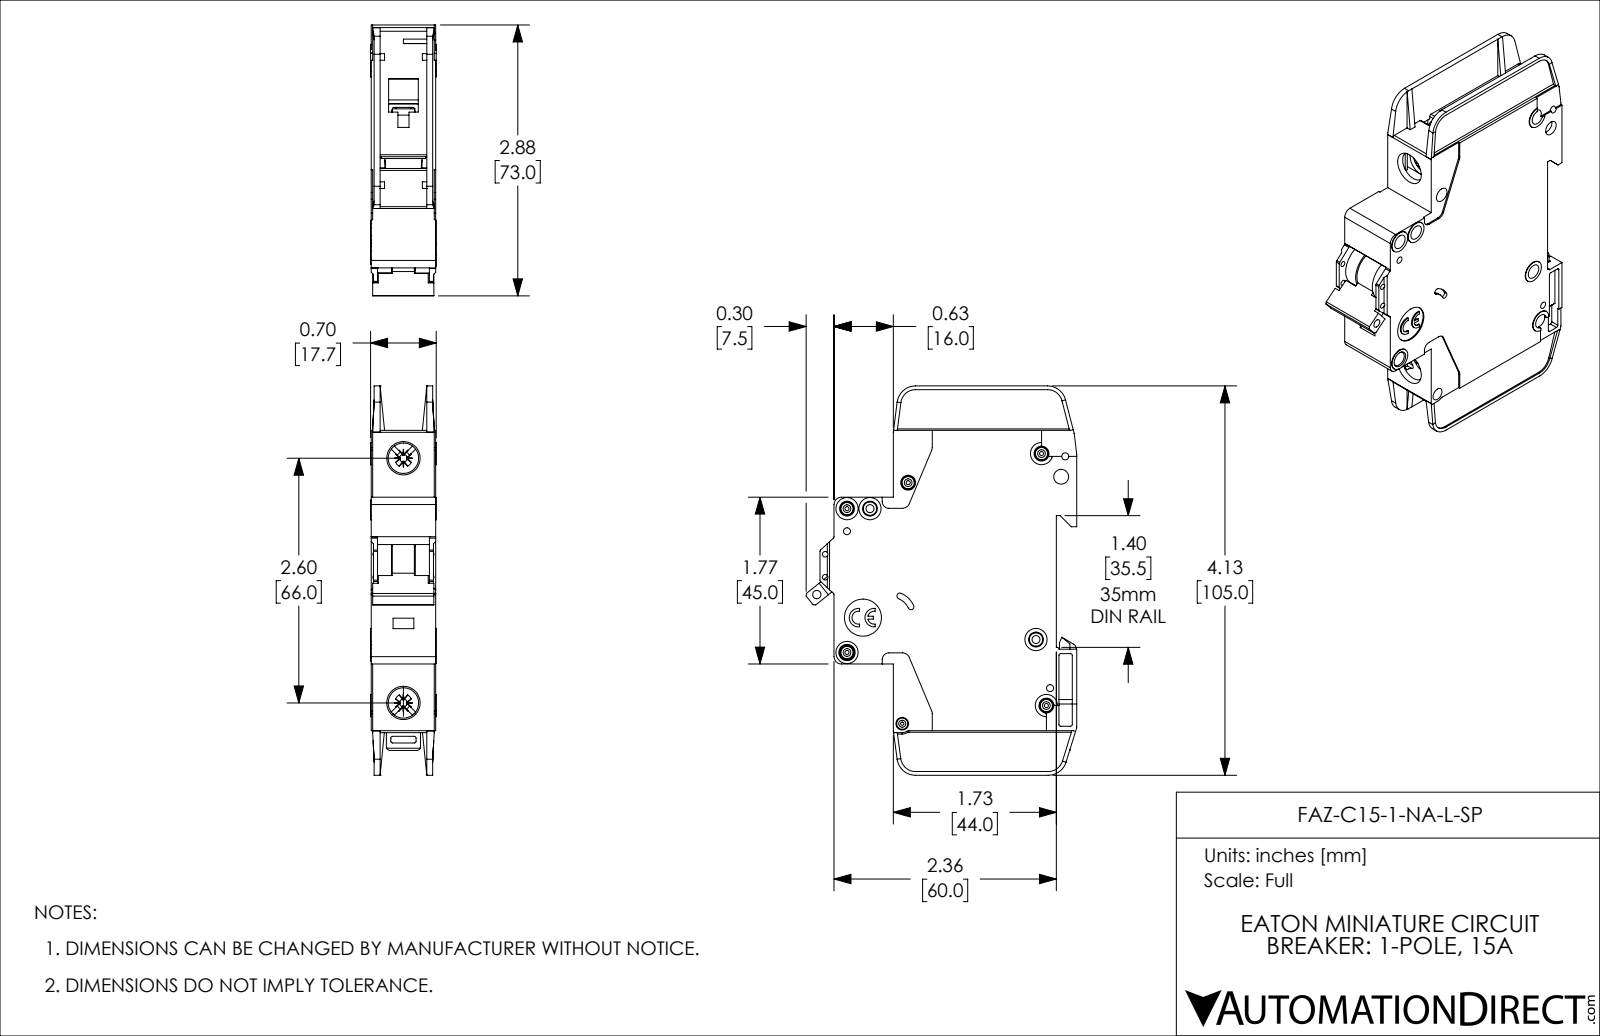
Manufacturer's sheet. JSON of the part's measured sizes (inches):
{"part_name": "FAZ-C15-1-NA-L-SP", "step_written_by": "SolidWorks 2019 (AUTOMOTIVE_DESIGN)", "units": "inches", "bodies": {"solids": 1, "faces": 1127, "planar": 671, "cylindrical": 357, "other": 99}, "overall_size": [4.134, 2.876, 0.697], "volume_in3": 4.682, "surface_area_in2": 41.01, "round_holes": [[0.157, 8], [0.043, 5], [0.075, 4], [0.059, 2], [0.085, 2], [0.323, 2], [0.035, 1], [0.089, 1], [0.098, 1], [0.134, 1], [0.394, 1]], "round_bosses_or_shafts": [[0.13, 5], [0.236, 4], [0.118, 2], [0.098, 1]], "partial_cylinders_radius": [[0.02, 42], [0.016, 10], [0.039, 10], [0.079, 8], [0.197, 5], [0.008, 4], [0.026, 4], [0.043, 4]], "face_to_face_distances": [0.047, 0.685, 0.591, 0.638, 0.094, 0.543, 0.016, 0.031, 0.496, 0.575], "hole_center_spacings": [0.244, 0.537, 0.87, 0.189, 0.199, 0.204, 0.221, 0.24]}
